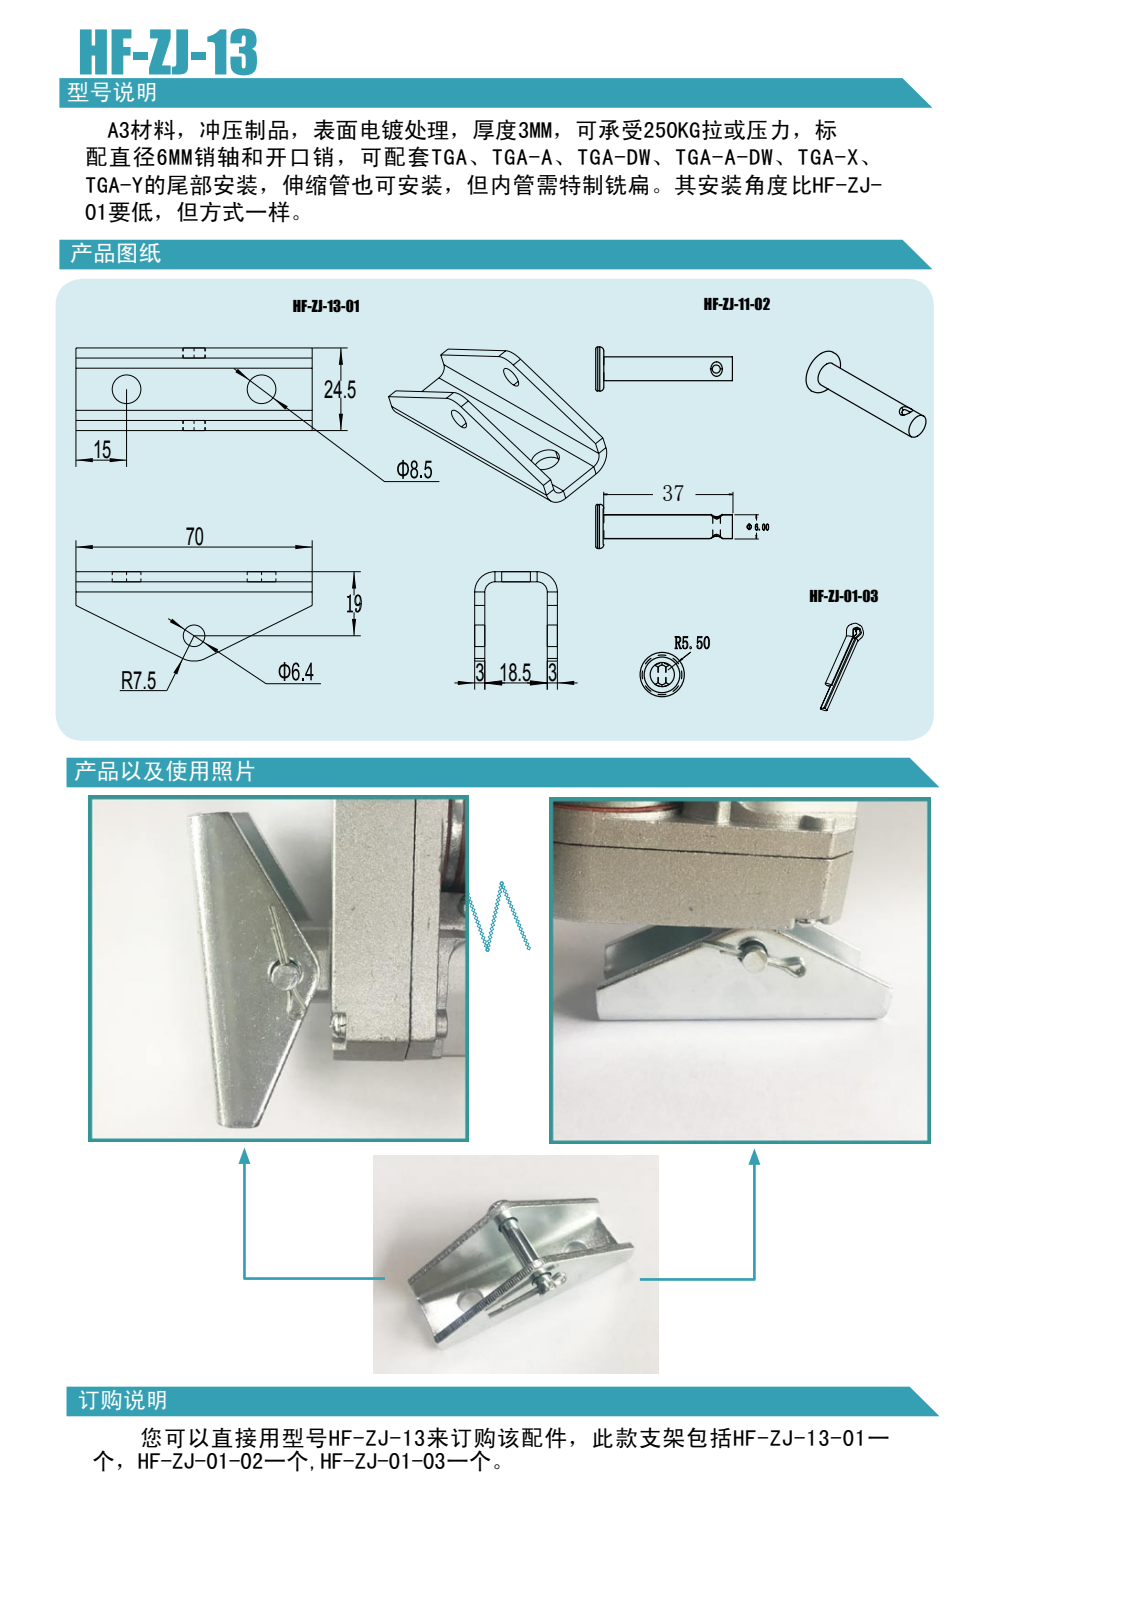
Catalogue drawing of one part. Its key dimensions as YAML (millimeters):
part_name: "ZJ-14"
step_written_by: "PRO/ENGINEER BY PARAMETRIC TECHNOLOGY CORPORATION, 2008380 (CONFIG_CONTROL_DESIGN)"
units: millimeters
bodies: {solids: 1, faces: 34, planar: 20, cylindrical: 14, other: 0}
overall_size: [1778, 673.1, 622.3]
volume: 170000000
surface_area: 5079000
round_holes:
  - {diameter: 215.9, count: 2}
  - {diameter: 162.56, count: 1}
partial_cylinders:
  - {radius: 76.2, count: 2}
  - {radius: 152.4, count: 2}
  - {radius: 190.5, count: 1}
face_to_face_distances: [76.2, 546.1, 622.3, 469.9, 1778]
hole_center_spacings: [1016]
